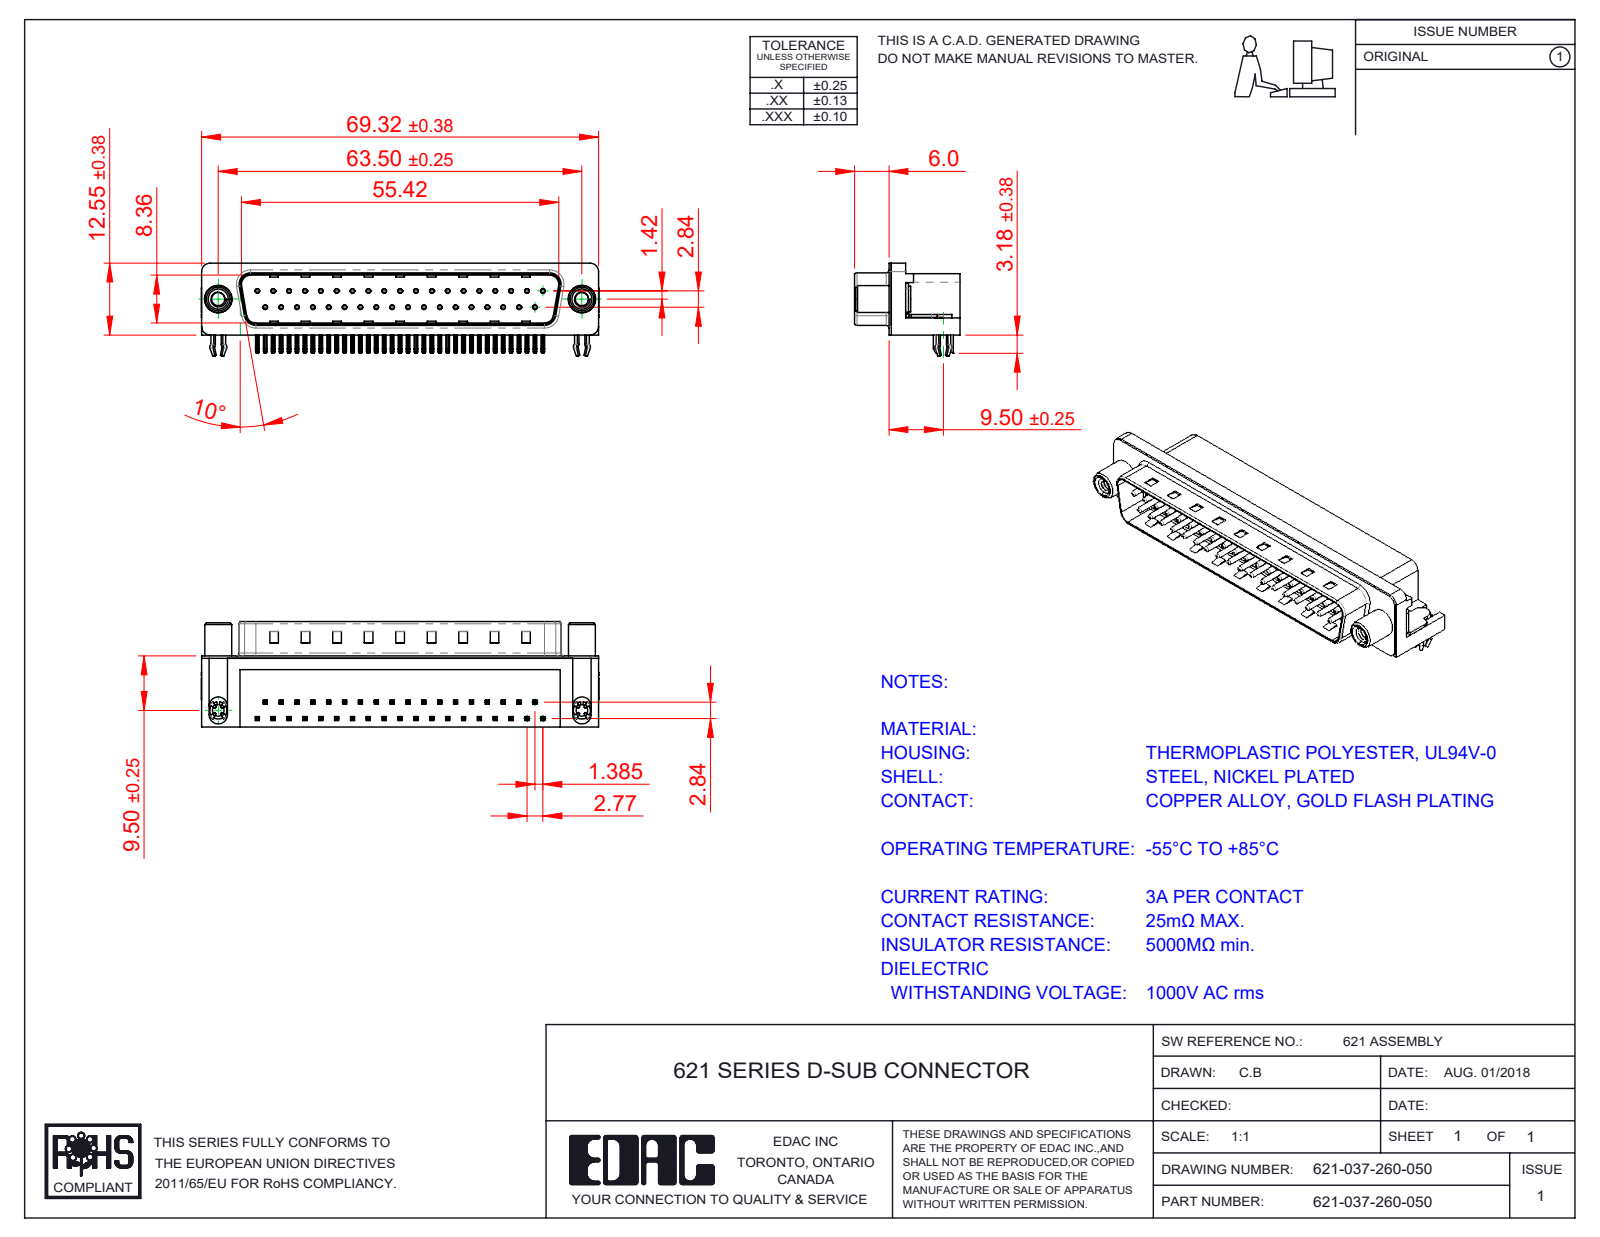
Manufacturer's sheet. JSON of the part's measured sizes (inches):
{"part_name": "621 Contact Bottom; 621 Contact Top; 621 4-40 Threaded Board Mount; 621 Shell_37 Socket (+3 more)", "step_written_by": "SolidWorks 2016 (CONFIG_CONTROL_DESIGN)", "units": "inches", "bodies": {"solids": 43, "faces": 3223, "planar": 2005, "cylindrical": 935, "other": 283}, "overall_size": [2.732, 0.724, 0.619], "volume_in3": 0.532, "surface_area_in2": 16.08, "round_holes": [[0.014, 37], [0.031, 37], [0.089, 2], [0.091, 2], [0.122, 2], [0.157, 2], [0.189, 2], [0.197, 2]], "round_bosses_or_shafts": [[0.03, 37], [0.193, 2], [0.185, 2], [0.177, 2], [0.152, 2], [0.128, 2]], "partial_cylinders_radius": [[0.01, 148], [0.005, 74], [0.039, 16], [0.02, 9], [0.063, 8], [0.059, 7], [0.035, 4], [0.079, 4]], "face_to_face_distances": [0.016, 0.472, 0.407, 0.345, 0.083, 0.067, 0.412, 0.428, 0.354, 0.488], "hole_center_spacings": [0.124, 0.109, 0.218, 0.327, 0.436, 0.545, 0.763, 0.872]}
